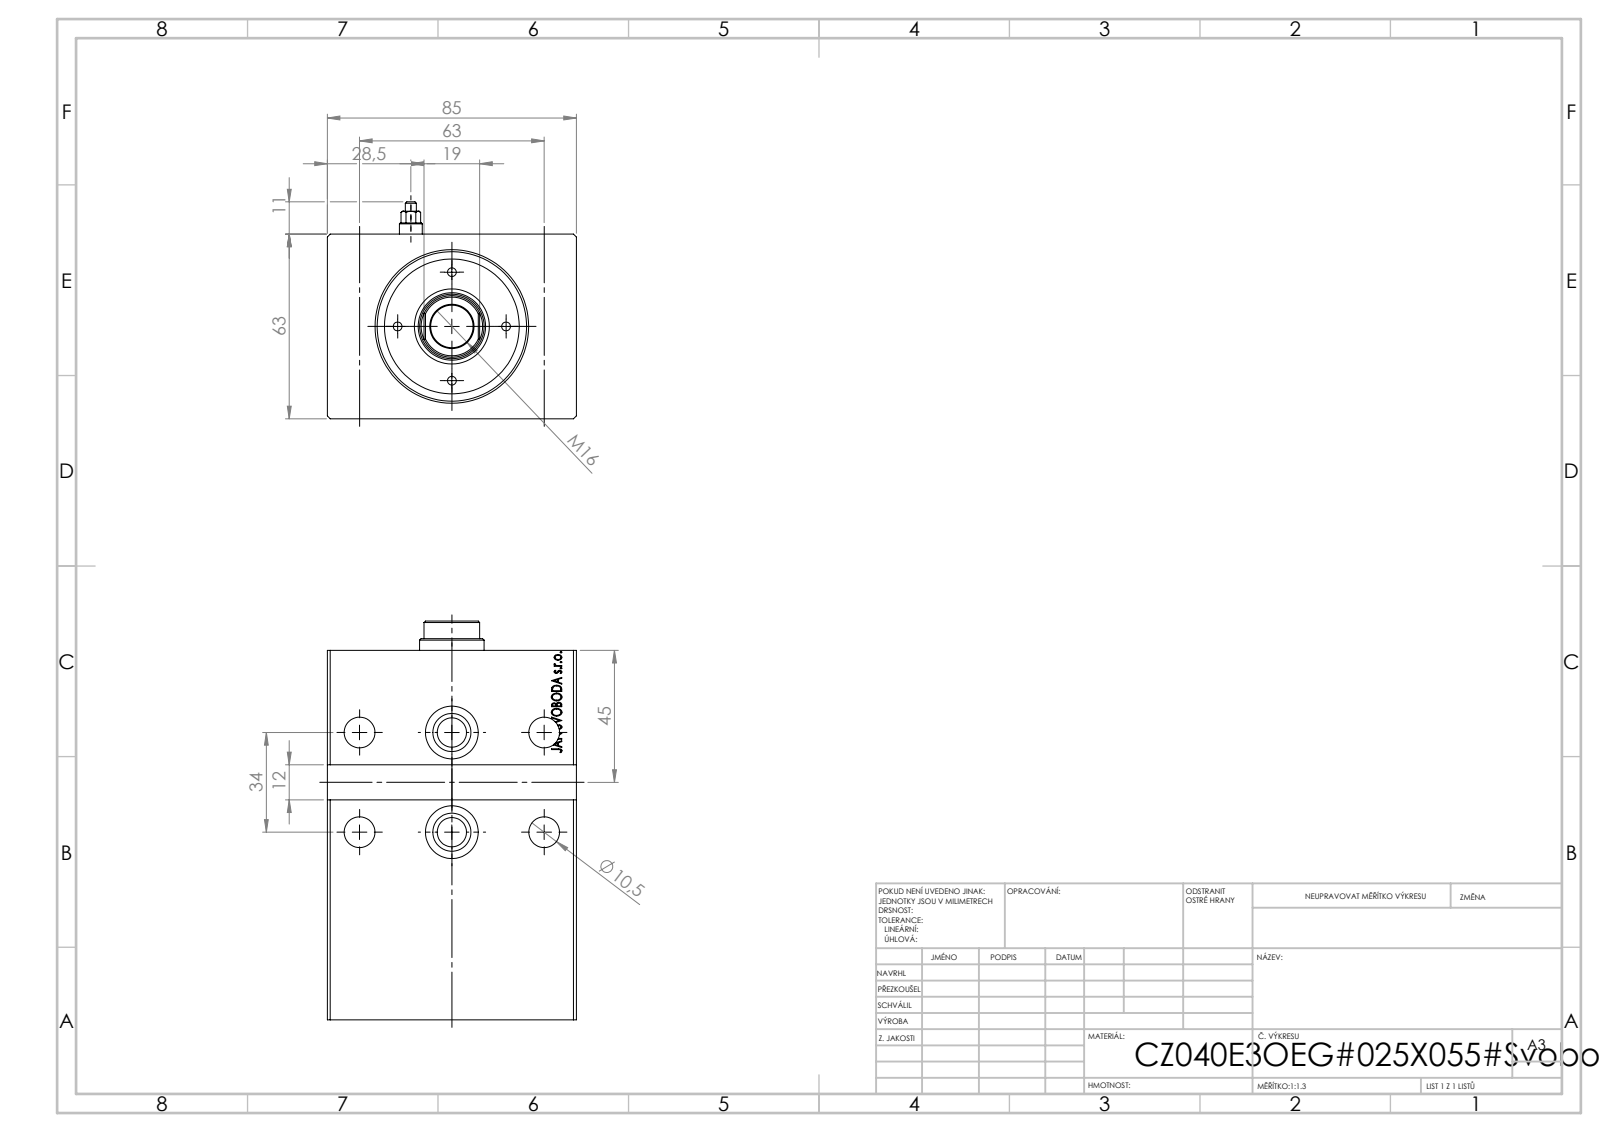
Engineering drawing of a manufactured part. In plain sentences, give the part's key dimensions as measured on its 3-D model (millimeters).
Its 3-D file was written by "SolidWorks 2019 (CONFIG_CONTROL_DESIGN)". It is 0 solids with 772 faces: 379 planar, 30 cylindrical and 363 other. Overall it measures 126 by 85 by 63 millimeters. Round holes: 4 of diameter 10.5, 2 of diameter 8, 2 of diameter 10, 2 of diameter 18, 1 of diameter 36, 1 of diameter 40, 1 of diameter 51. Round bosses or shafts: 2 of diameter 13. The main face-to-face distances are 63, 85, 126, 110.7, 15.3, 2, 61, 125.8, 15.1, 10. The hole center spacings are 31.5, 46.35, 34, 63, 71.59, 15.65, 18.85, 30.41.
